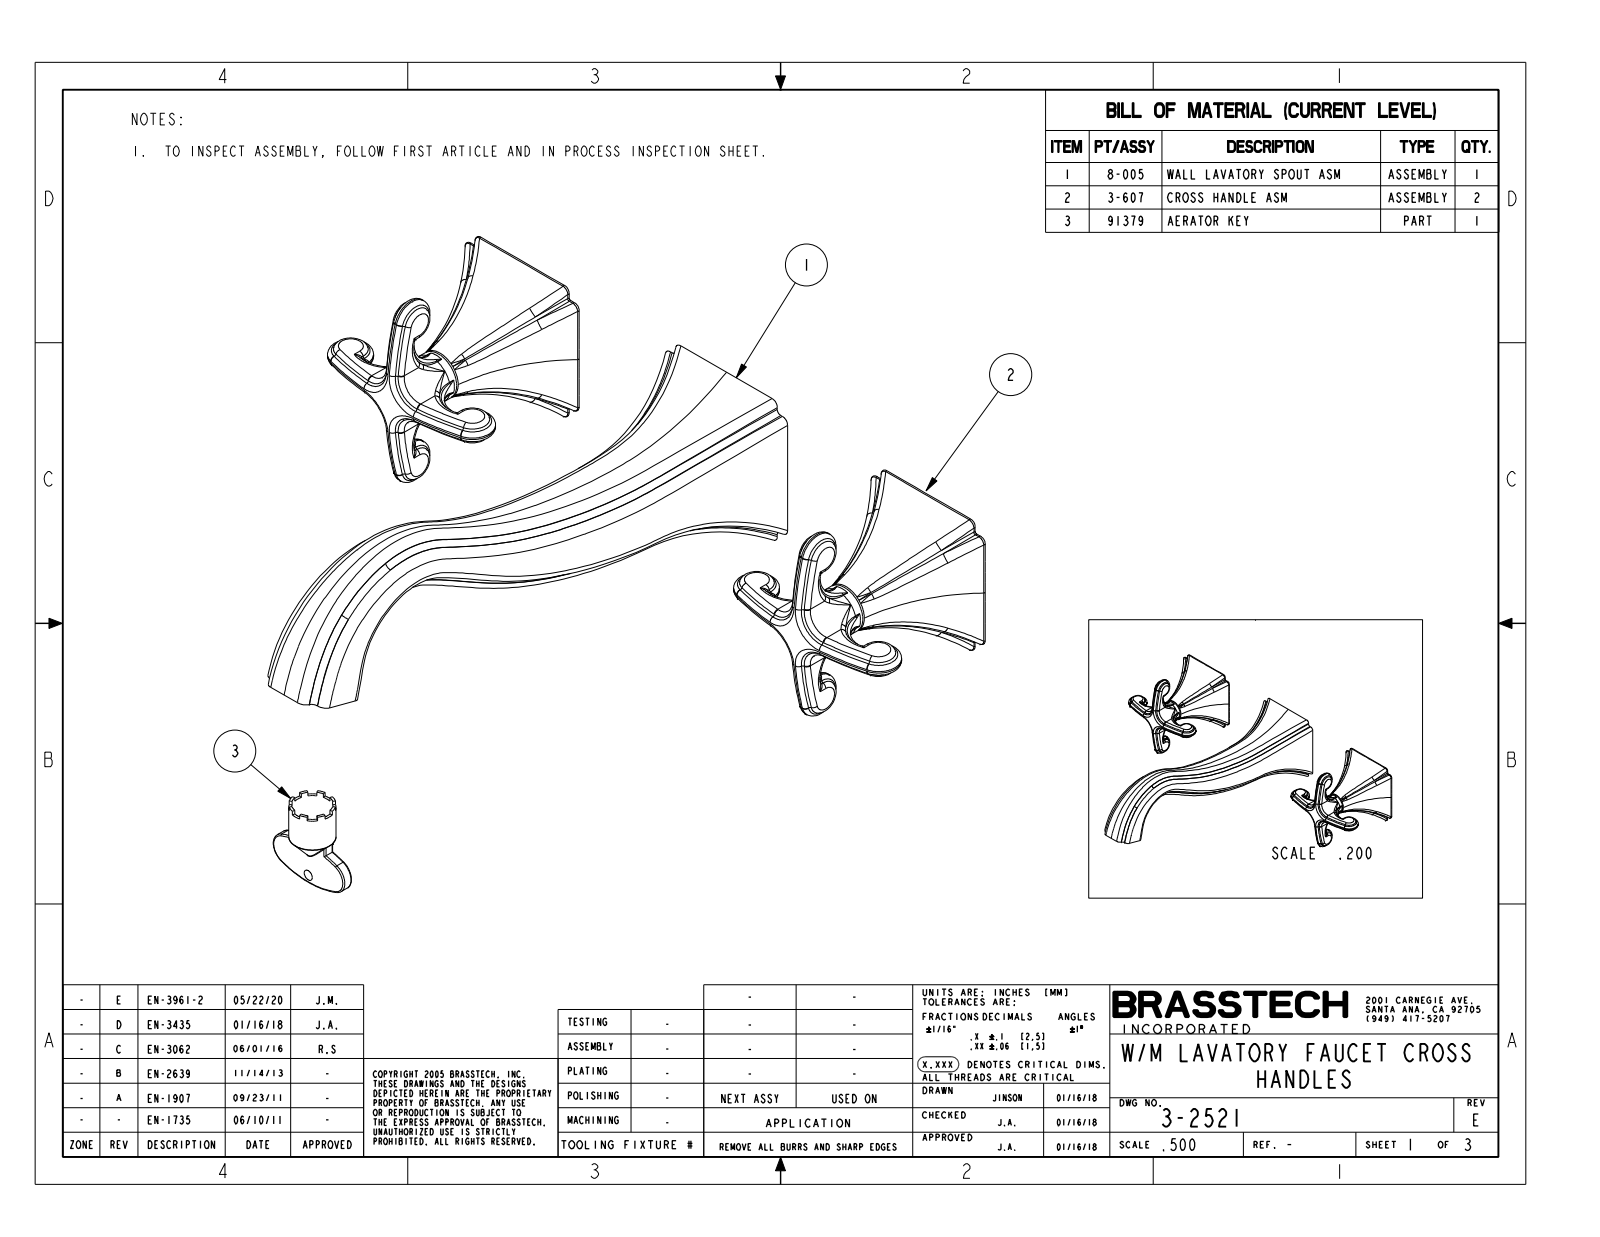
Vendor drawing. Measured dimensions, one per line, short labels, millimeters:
name: 3-2521_SW0001
written by: CREO PARAMETRIC BY PTC INC, 2018400 (AUTOMOTIVE_DESIGN)
unit: mm
bodies: 3 solids, 667 faces (30 planar, 72 cylindrical, 565 other)
size: 276.2 × 218.4 × 80.7
volume: 312 200 mm³; area: 62 810 mm²
holes: 2× ⌀40.1
bosses: 2× ⌀52.1, 2× ⌀18, 1× ⌀12.9, 1× ⌀12.3
rounds: 32× R1, 16× R1.8, 8× R8.1
face distances: 0.5, 0.3, 0.4, 8, 8, 200, 41.8, 41, 0.8, 192
hole spacings: 200
